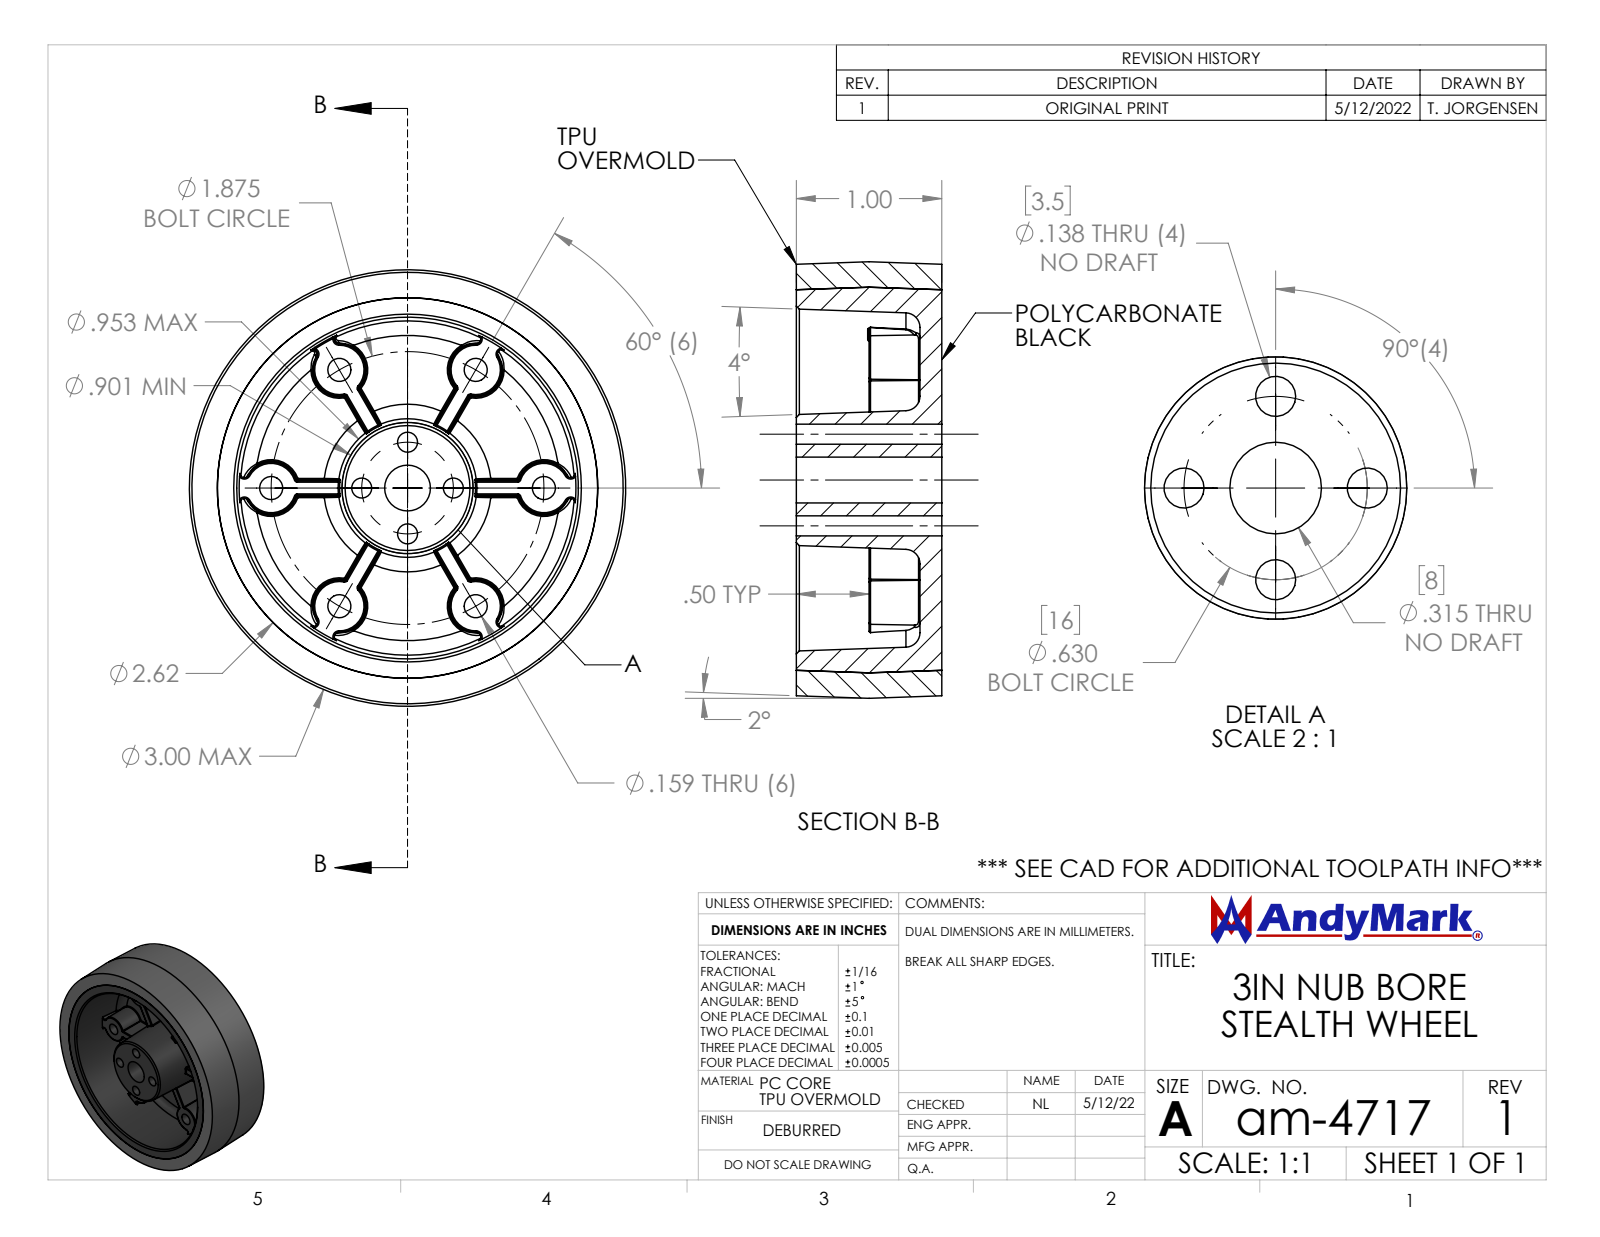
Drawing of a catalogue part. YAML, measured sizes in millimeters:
part_name: "3in Wheel Intergrated 8mm Hub; 3in Tread; am-4717 3in Stealth Wheel Nub Bore"
step_written_by: "SolidWorks 2024 (CONFIG_CONTROL_DESIGN)"
units: millimeters
bodies: {solids: 2, faces: 293, planar: 29, cylindrical: 57, other: 207}
overall_size: [76.2, 76.2, 25.4]
volume: 66660
surface_area: 34790
round_holes:
  - {diameter: 4, count: 6}
  - {diameter: 3.5, count: 4}
partial_cylinders:
  - {radius: 0.3, count: 12}
  - {radius: 0.8, count: 10}
face_to_face_distances: [25.4, 3.8, 21.6, 12.7, 8.9]
hole_center_spacings: [23.8, 41.2, 11.3, 17.3, 21, 25.1, 28.7, 31]
